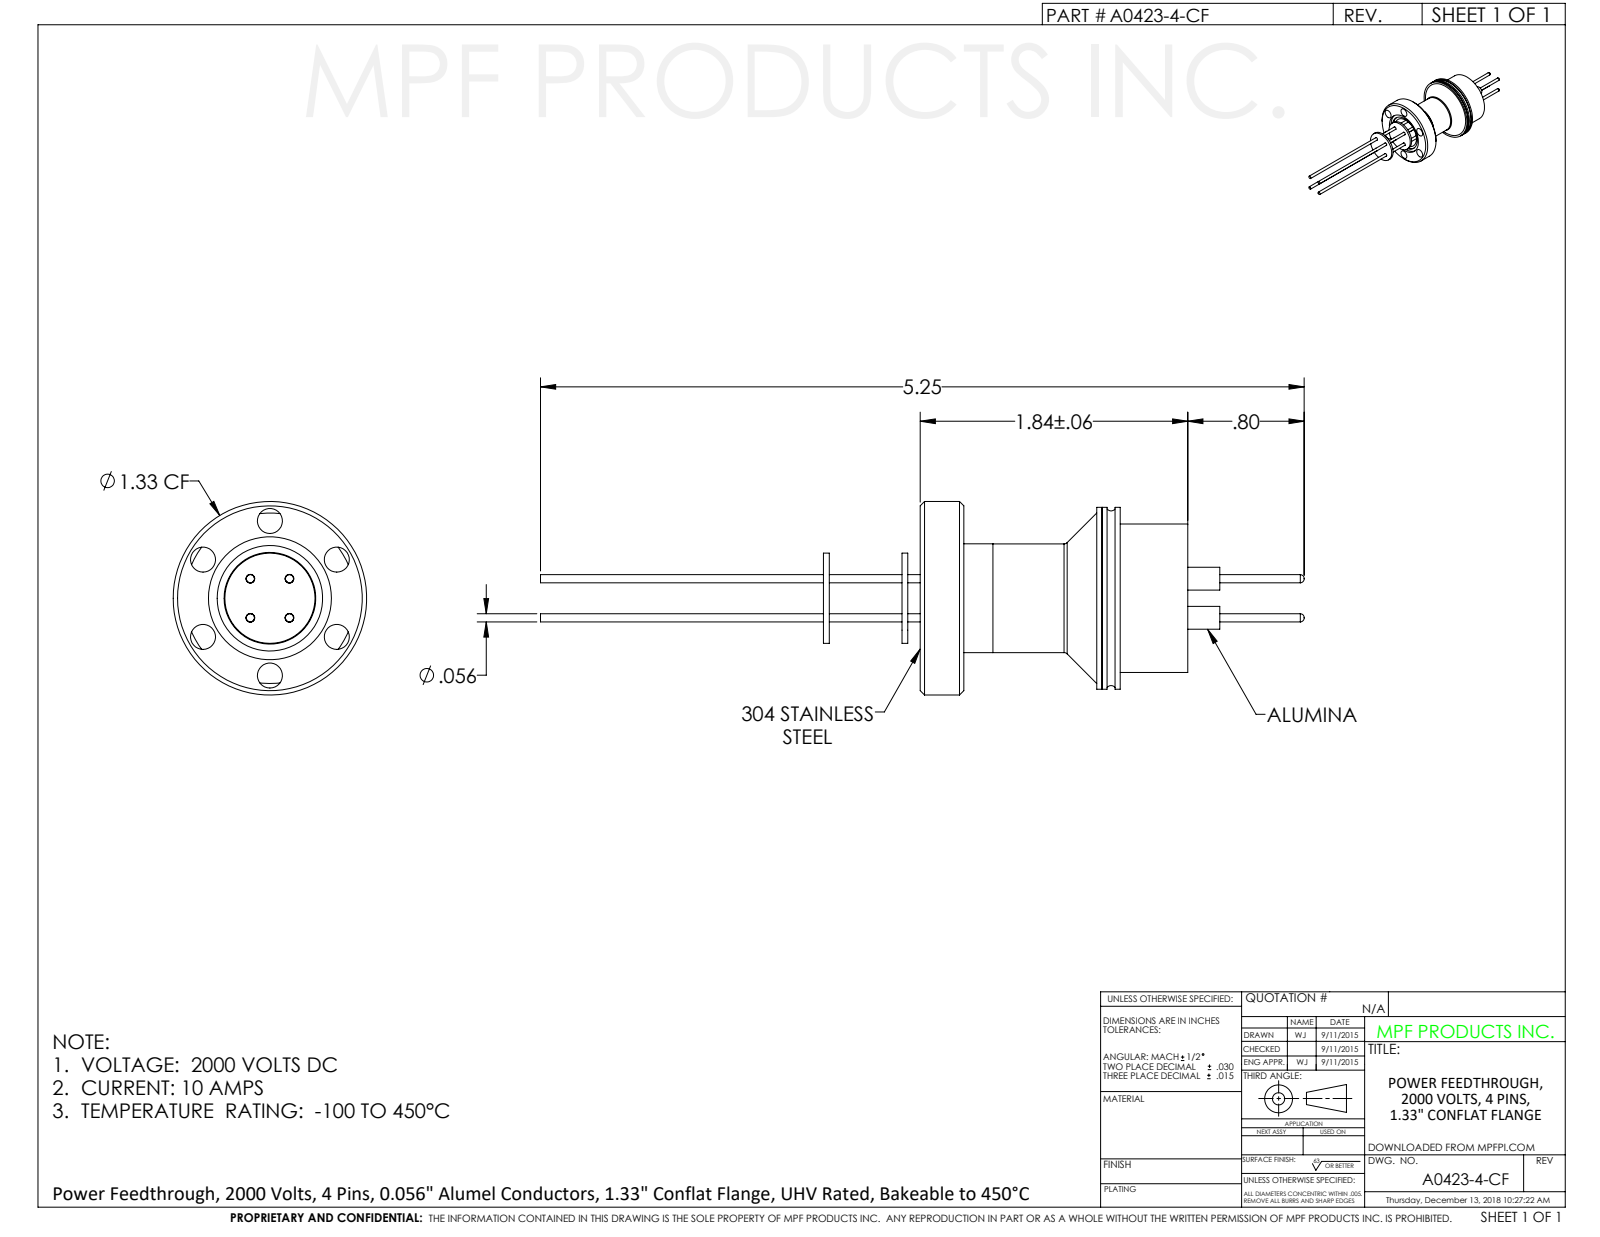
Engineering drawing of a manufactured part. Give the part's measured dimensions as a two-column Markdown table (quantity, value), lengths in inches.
| quantity | value |
| --- | --- |
| part name | A0423-4-CF |
| STEP written by | SolidWorks 2012 (CONFIG_CONTROL_DESIGN) |
| units | inches |
| bodies | 1 solid, 207 faces (44 planar, 110 cylindrical, 53 other) |
| overall size | 5.25 × 1.33 × 1.33 |
| volume | 0.623 in³ |
| surface area | 22.12 in² |
| round holes (diameter × count) | 0.172 × 6, 0.159 × 4, 0.63 × 1, 0.675 × 1, 0.725 × 1, 0.845 × 1, 0.94 × 1, 0.96 × 1, 0.97 × 1 |
| round bosses / shafts (diameter × count) | 0.187 × 4, 0.171 × 4, 0.056 × 4, 1.33 × 1, 1.25 × 1, 1.02 × 1, 0.957 × 1, 0.748 × 1 |
| main face-to-face distances | 0.04, 1.52, 0.05, 1.47, 0.601, 1.805, 1.755, 0.285, 0.43, 0.38 |
| hole center spacings | 0.531, 0.92, 0.19, 0.269, 0.351, 0.419, 0.515, 0.608 |
